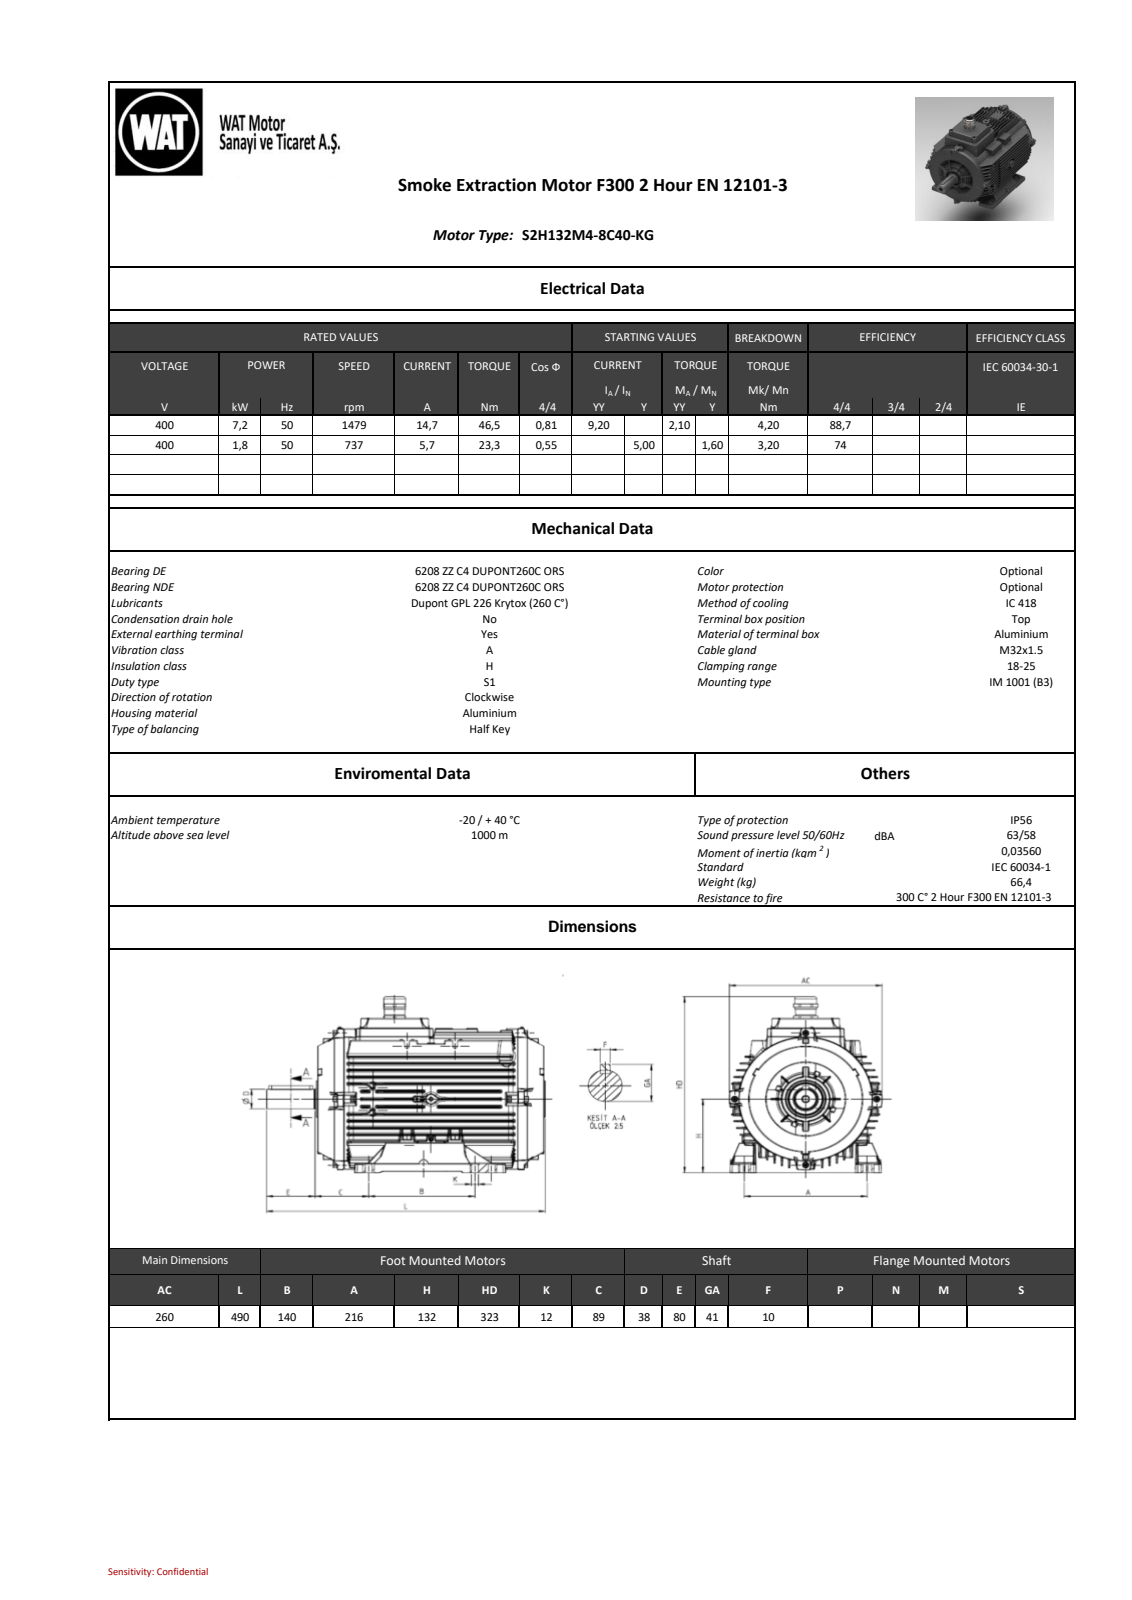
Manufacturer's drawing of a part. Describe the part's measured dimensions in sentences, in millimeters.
The part is named "260314206C66eedi". Its 3-D file was written by "SIEMENS PLM Software NX 11.0 (AP203_CONFIGURATION_CONTROLLED_3D_DESIGN_OF_MECHANICAL_PARTS_AND_ASSEMBLIES_MIM_LF)". It is 0 solids with 8089 faces: 1705 planar, 2802 cylindrical and 3582 other. Overall it measures 489.5 by 323.2 by 260 millimeters. Round holes: 3 of diameter 4.2, 2 of diameter 6.8, 2 of diameter 8, 1 of diameter 10.5, 1 of diameter 18, 1 of diameter 44, 1 of diameter 58.4, 1 of diameter 58.6. Round bosses or shafts: 4 of diameter 14.8, 4 of diameter 13, 4 of diameter 10, 1 of diameter 230.5, 1 of diameter 40, 1 of diameter 38, 1 of diameter 37.4, 1 of diameter 29.59. Partial cylindrical surfaces (rounded edges, fillets, slot ends): 1047 of radius 0.8, 696 of radius 1, 111 of radius 1.5, 70 of radius 0.5, 68 of radius 2, 22 of radius 3, 12 of radius 5, 10 of radius 0.1. The main face-to-face distances are 10.42, 10.56, 20.84, 10.28, 125.58, 84.04, 115.18, 104.9, 94.46, 10.4. The hole center spacings are 32, 261.49.
